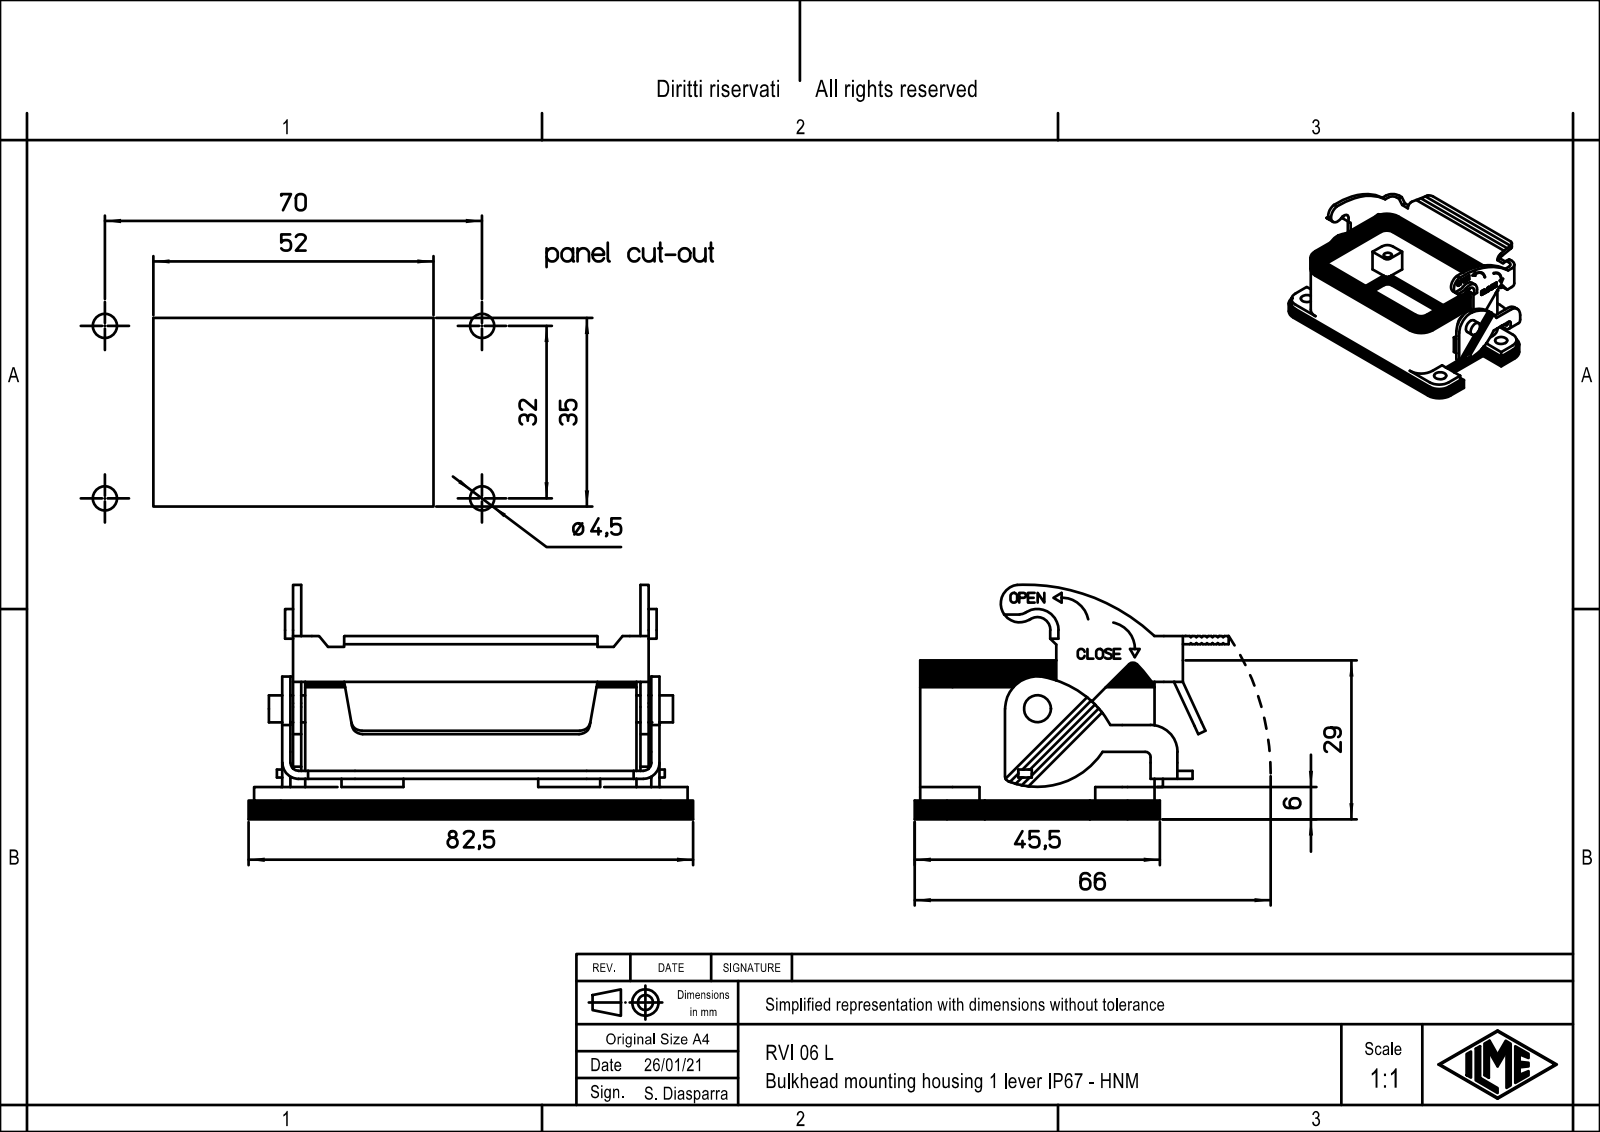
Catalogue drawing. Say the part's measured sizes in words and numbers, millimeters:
The part is named "RVI_06_L". Its 3-D file was written by "Creo Elements/Direct Modeling 20.1B 02-Apr-2019 (C) Parametric Technology GmbH (AUTOMOTIVE_DESIGN)". It is 1 solid with 413 faces: 296 planar, 117 cylindrical and 0 other. Overall it measures 82.5 by 58.25 by 43.5 millimeters. Its volume is 28 849 cubic millimeters and its surface area 24 197 square millimeters. Round holes: 4 of diameter 2.46, 4 of diameter 3, 4 of diameter 4.5. Round bosses or shafts: 1 of diameter 5. Partial cylindrical surfaces (rounded edges, fillets, slot ends): 13 of radius 2, 10 of radius 3, 9 of radius 6, 6 of radius 1, 6 of radius 1.5, 5 of radius 5, 4 of radius 6.1, 3 of radius 3.5. The main face-to-face distances are 1.5, 3, 40.5, 3.5, 4, 0.5, 2, 66.5, 6, 62.25. The hole center spacings are 13.24, 32.24, 57.05, 64.18, 27, 32, 44, 51.62.
